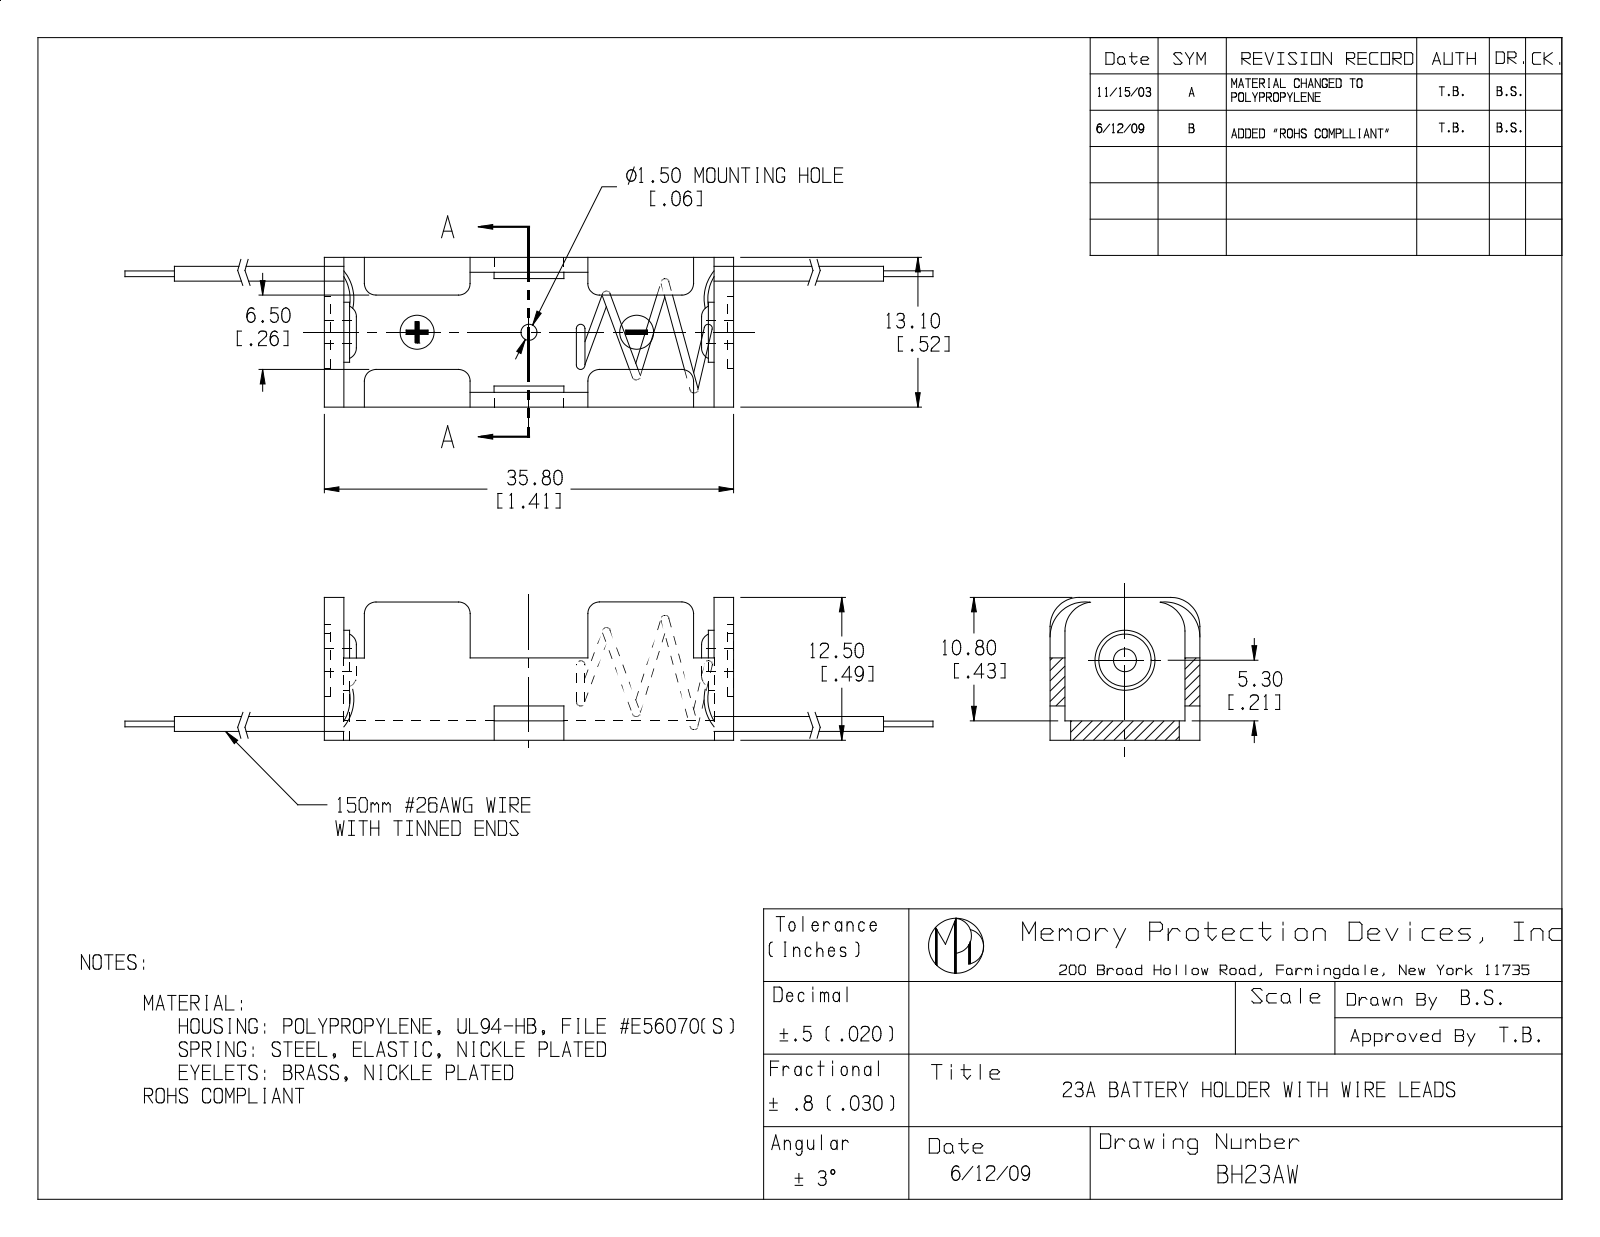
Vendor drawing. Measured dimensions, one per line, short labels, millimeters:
name: BH23AW
written by: SolidWorks 2017 (AUTOMOTIVE_DESIGN)
unit: mm
bodies: 7 solids, 131 faces (57 planar, 53 cylindrical, 21 other)
size: 347.8 × 13.1 × 12.5
volume: 2 452 mm³; area: 4 536 mm²
holes: 1× ⌀1.2, 1× ⌀1.5, 1× ⌀2, 1× ⌀7
bosses: 1× ⌀5.25, 1× ⌀1.5, 1× ⌀0.66, 1× ⌀0.5
rounds: 4× R1, 2× R2.55, 2× R2.59, 2× R3.08
face distances: 1.3, 11.8, 1.7, 13.1, 1.8, 34, 10.5, 32.2, 35.8, 35.5
